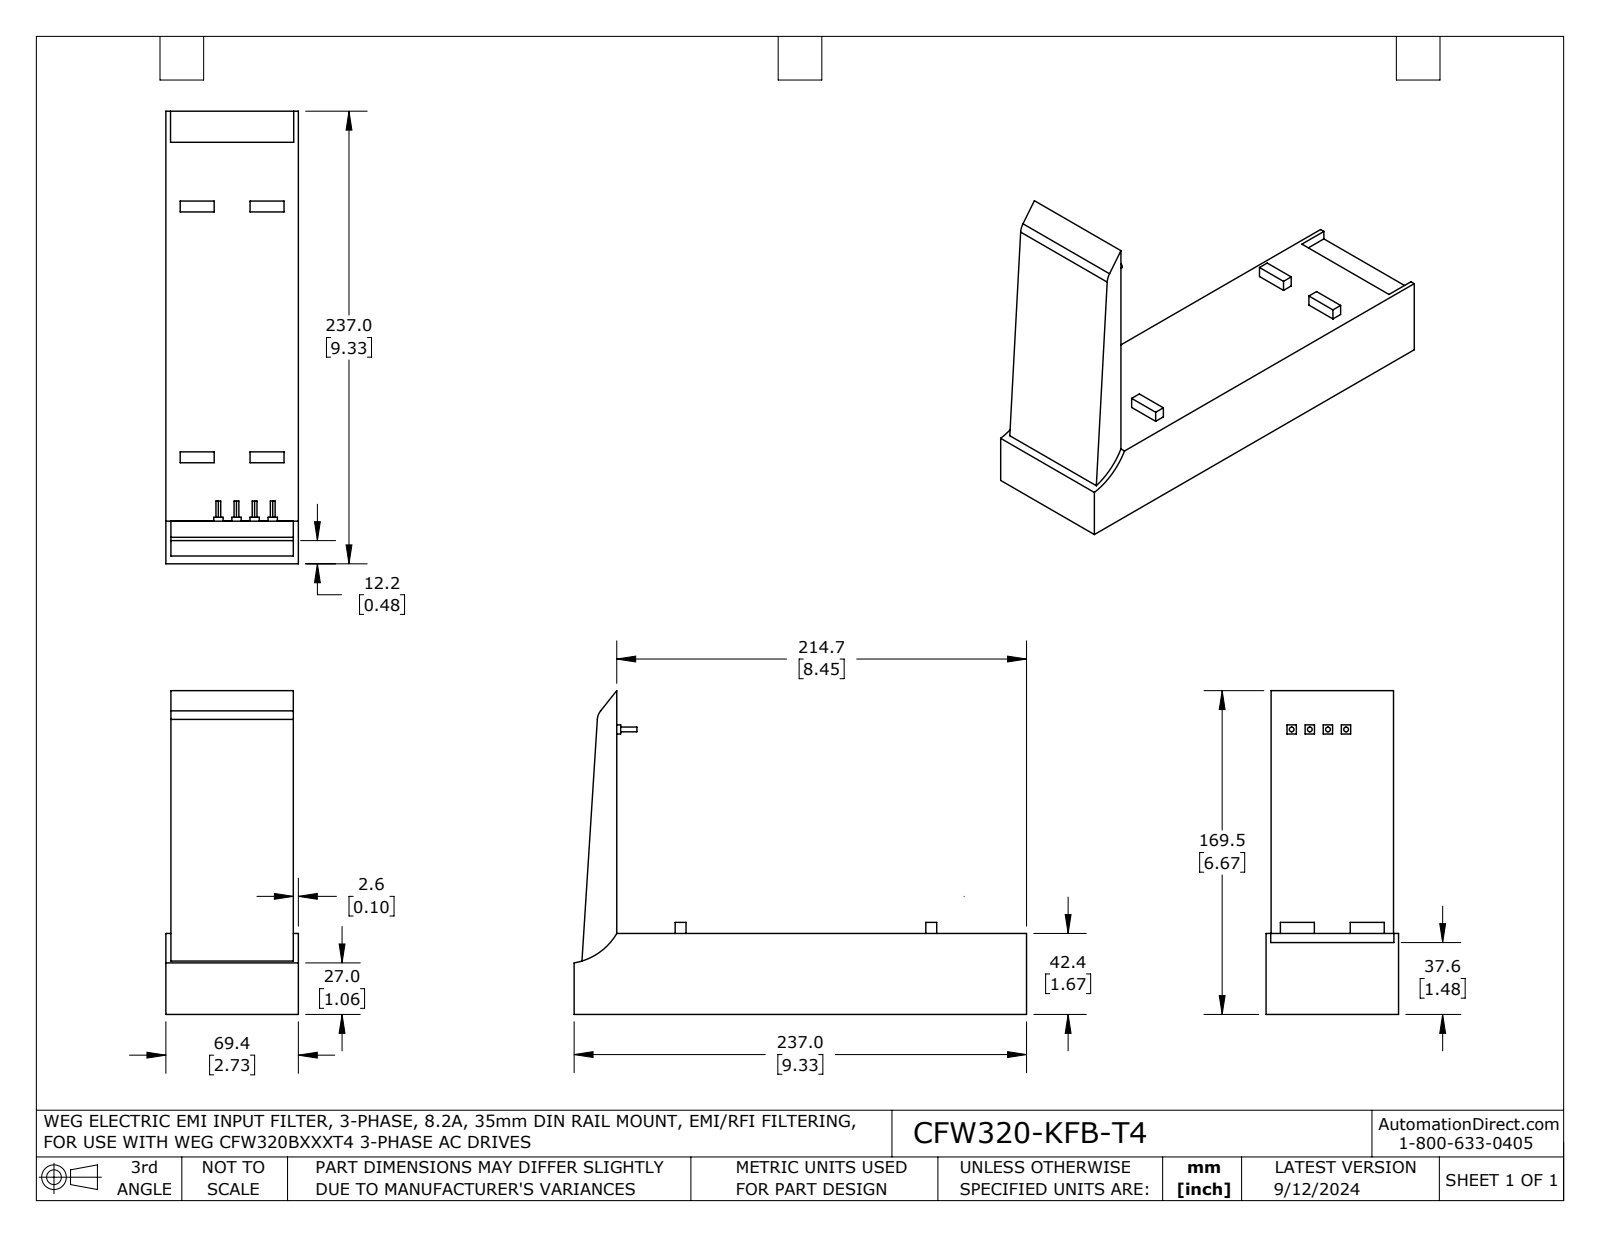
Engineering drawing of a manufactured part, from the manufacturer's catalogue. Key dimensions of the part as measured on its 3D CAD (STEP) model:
Part name (STEP PRODUCT): CFW320-KFB-T4
STEP written by: SolidWorks 2021 (AUTOMOTIVE_DESIGN)
Units: inches
Bodies: 1 solid, 69 faces (59 planar, 10 cylindrical, 0 other)
Overall size (bounding box): 9.331 × 6.675 × 2.732
Volume: 48.45 in³ · Surface area: 122.4 in²
Round bosses / shafts (diameter × count): ⌀0.098 ×4
Partial cylindrical surfaces — rounded edges, fillets, slot ends (radius × count): R0.315 ×1, R1.26 ×1
Main face-to-face distances: 1.669, 2.733, 8.452, 9.331, 0.879, 0.104, 2.628, 2.629, 2.524, 0.104
